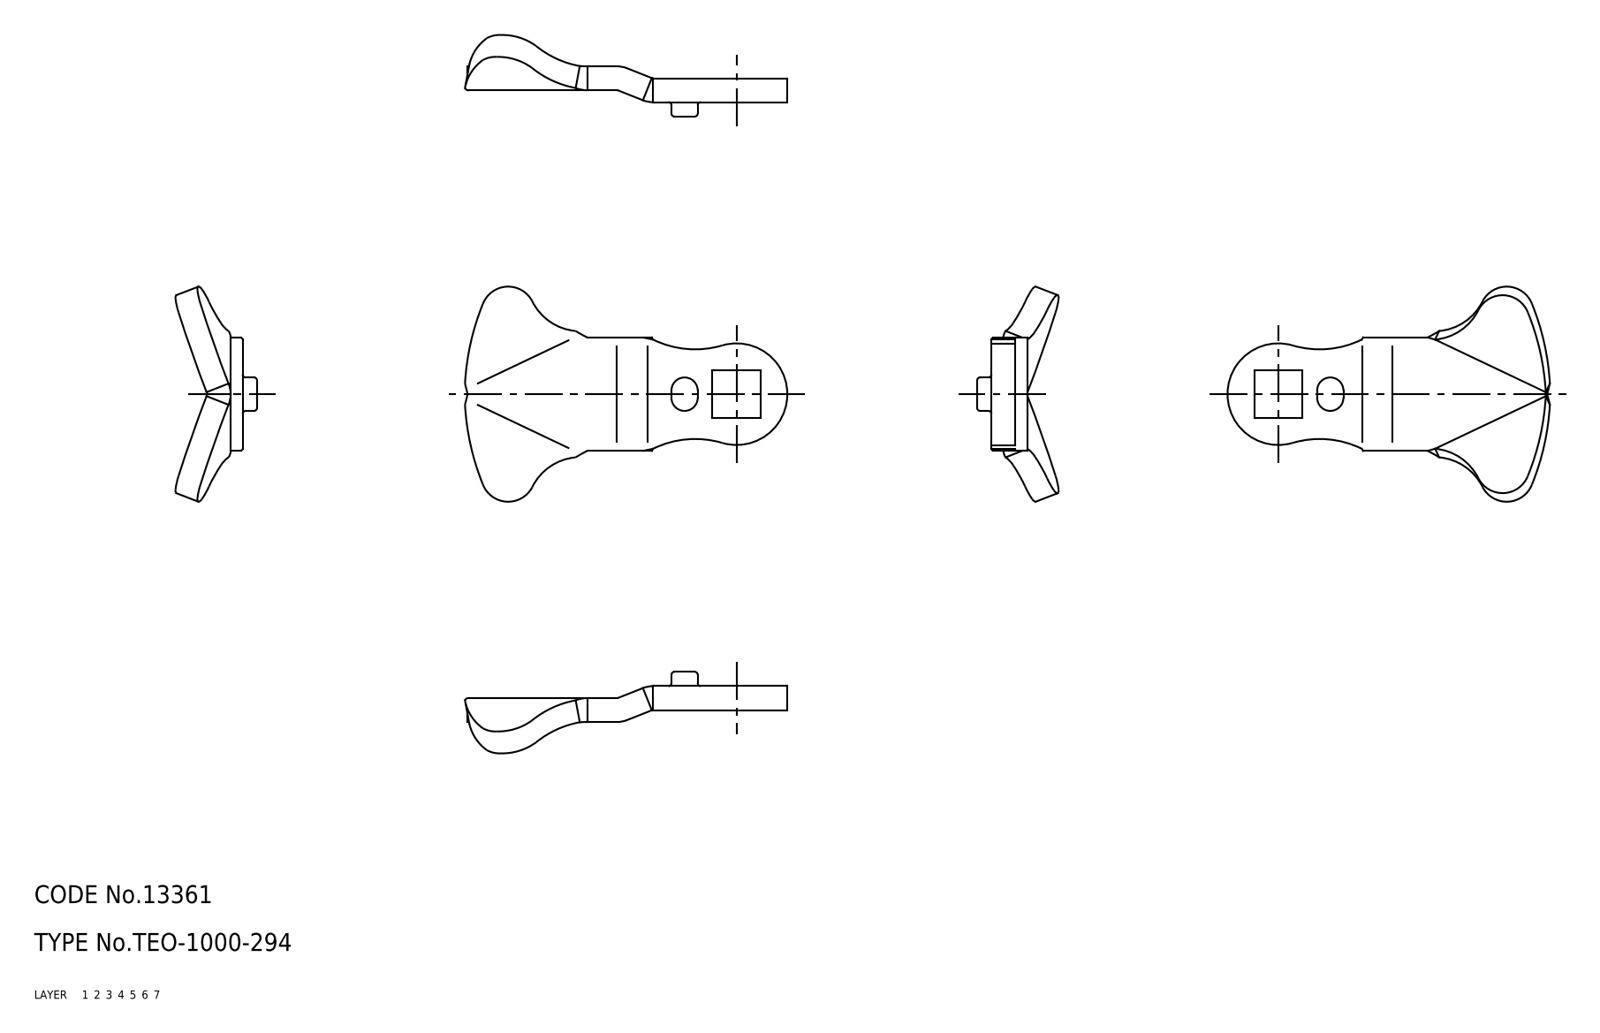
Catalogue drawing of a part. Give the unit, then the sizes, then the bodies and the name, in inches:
Units: inches
Overall size (bounding box): 2.12 × 1.417 × 0.586
Volume: 0.266 in³ · Surface area: 4.689 in²
Bodies: 1 solid, 59 faces (0 planar, 0 cylindrical, 59 other)
Part name (STEP PRODUCT): cam
STEP written by: CADfix (AUTOMOTIVE_DESIGN)
